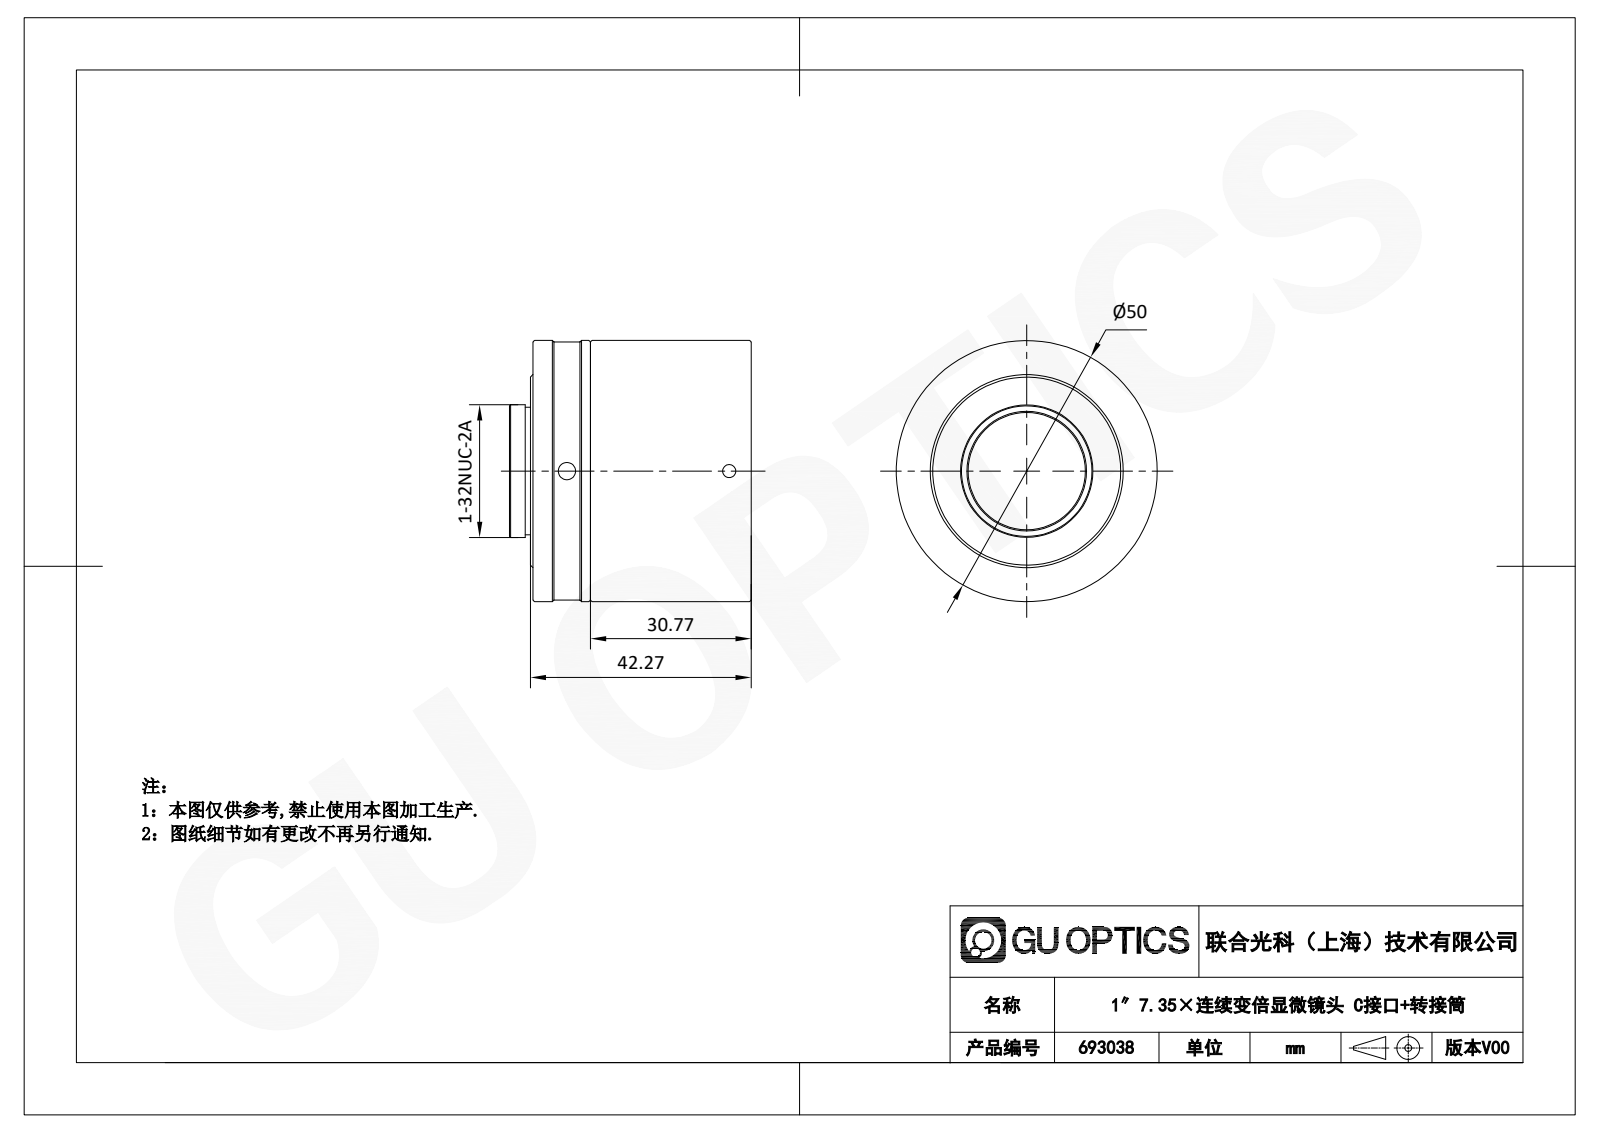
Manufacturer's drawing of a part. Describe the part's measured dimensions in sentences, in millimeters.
The part is named "693038". Its 3-D file was written by "SolidWorks 2020 (CONFIG_CONTROL_DESIGN)". It is 2 solids with 153 faces: 65 planar, 21 cylindrical and 67 other. Overall it measures 50 by 50 by 46.27 millimeters. Its volume is 34 076 cubic millimeters and its surface area 22 045 square millimeters. Round holes: 3 of diameter 2.5, 3 of diameter 3.3, 1 of diameter 22.5, 1 of diameter 35.8, 1 of diameter 41.25, 1 of diameter 42.25, 1 of diameter 43.8, 1 of diameter 44. Round bosses or shafts: 1 of diameter 50, 1 of diameter 49.4, 1 of diameter 42.8, 1 of diameter 25.4, 1 of diameter 24.4. The main face-to-face distances are 2, 9, 0.5, 2.5, 11, 11.5, 18.27, 3, 30.77, 8.5. The hole center spacings are 31.07.
